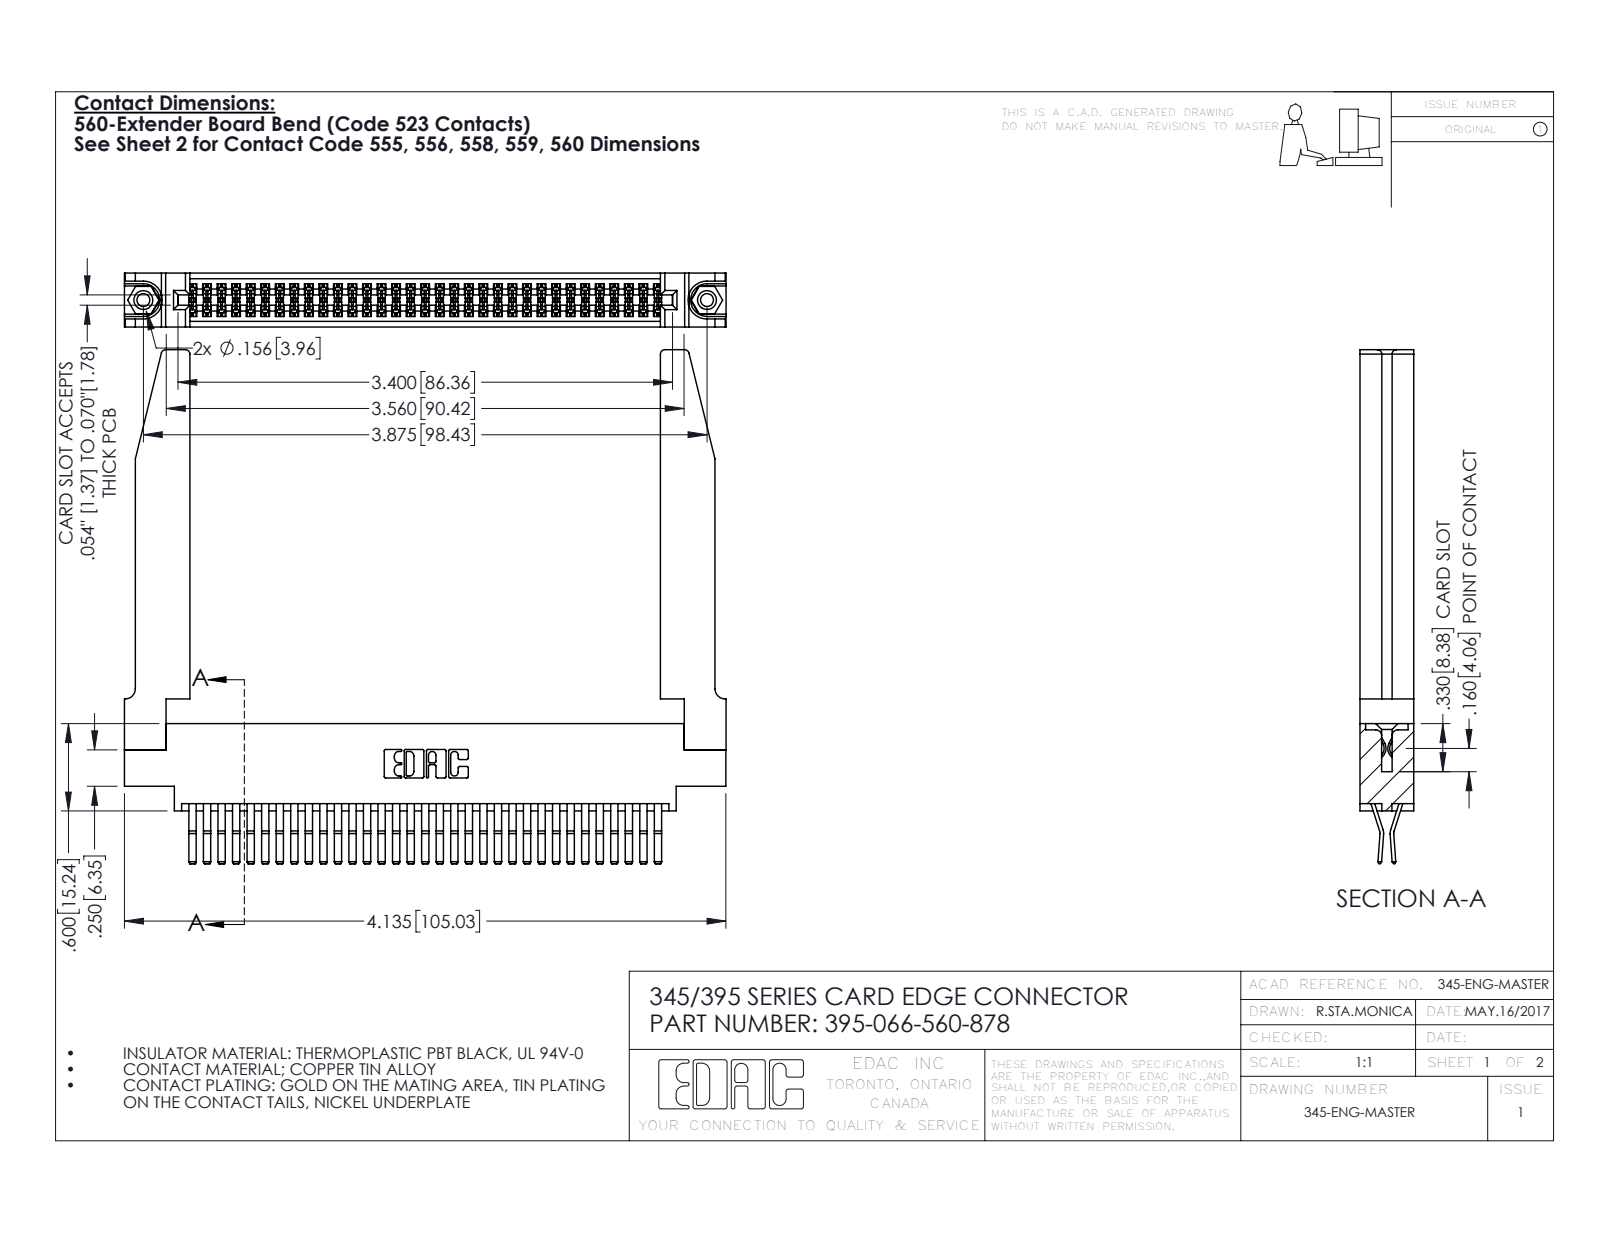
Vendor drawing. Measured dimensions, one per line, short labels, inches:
name: 345-292-001_560 Tail; 345 Part_0.170 Offset - 0.156 Dia-TH; 345-250-001_345-250-001-102; 395-066-560-878 (+1 more)
written by: SolidWorks 2016 (CONFIG_CONTROL_DESIGN)
unit: in
bodies: 71 solids, 3796 faces (2404 planar, 1340 cylindrical, 52 other)
size: 4.136 × 3.532 × 0.37
volume: 1.111 in³; area: 36.2 in²
holes: 2× ⌀0.089, 2× ⌀0.125, 2× ⌀0.156, 1× ⌀0.064
bosses: 2× ⌀0.155
rounds: 100× R0.006, 22× R0.01, 8× R0.03, 6× R0.007, 6× R0.031, 3× R0.026, 2× R0.01, 2× R0.014
face distances: 0.37, 0.072, 0.298, 0.025, 0.098, 0.272, 0.2, 0.225, 0.148, 0.15
hole spacings: 0.27, 3.64, 3.875
